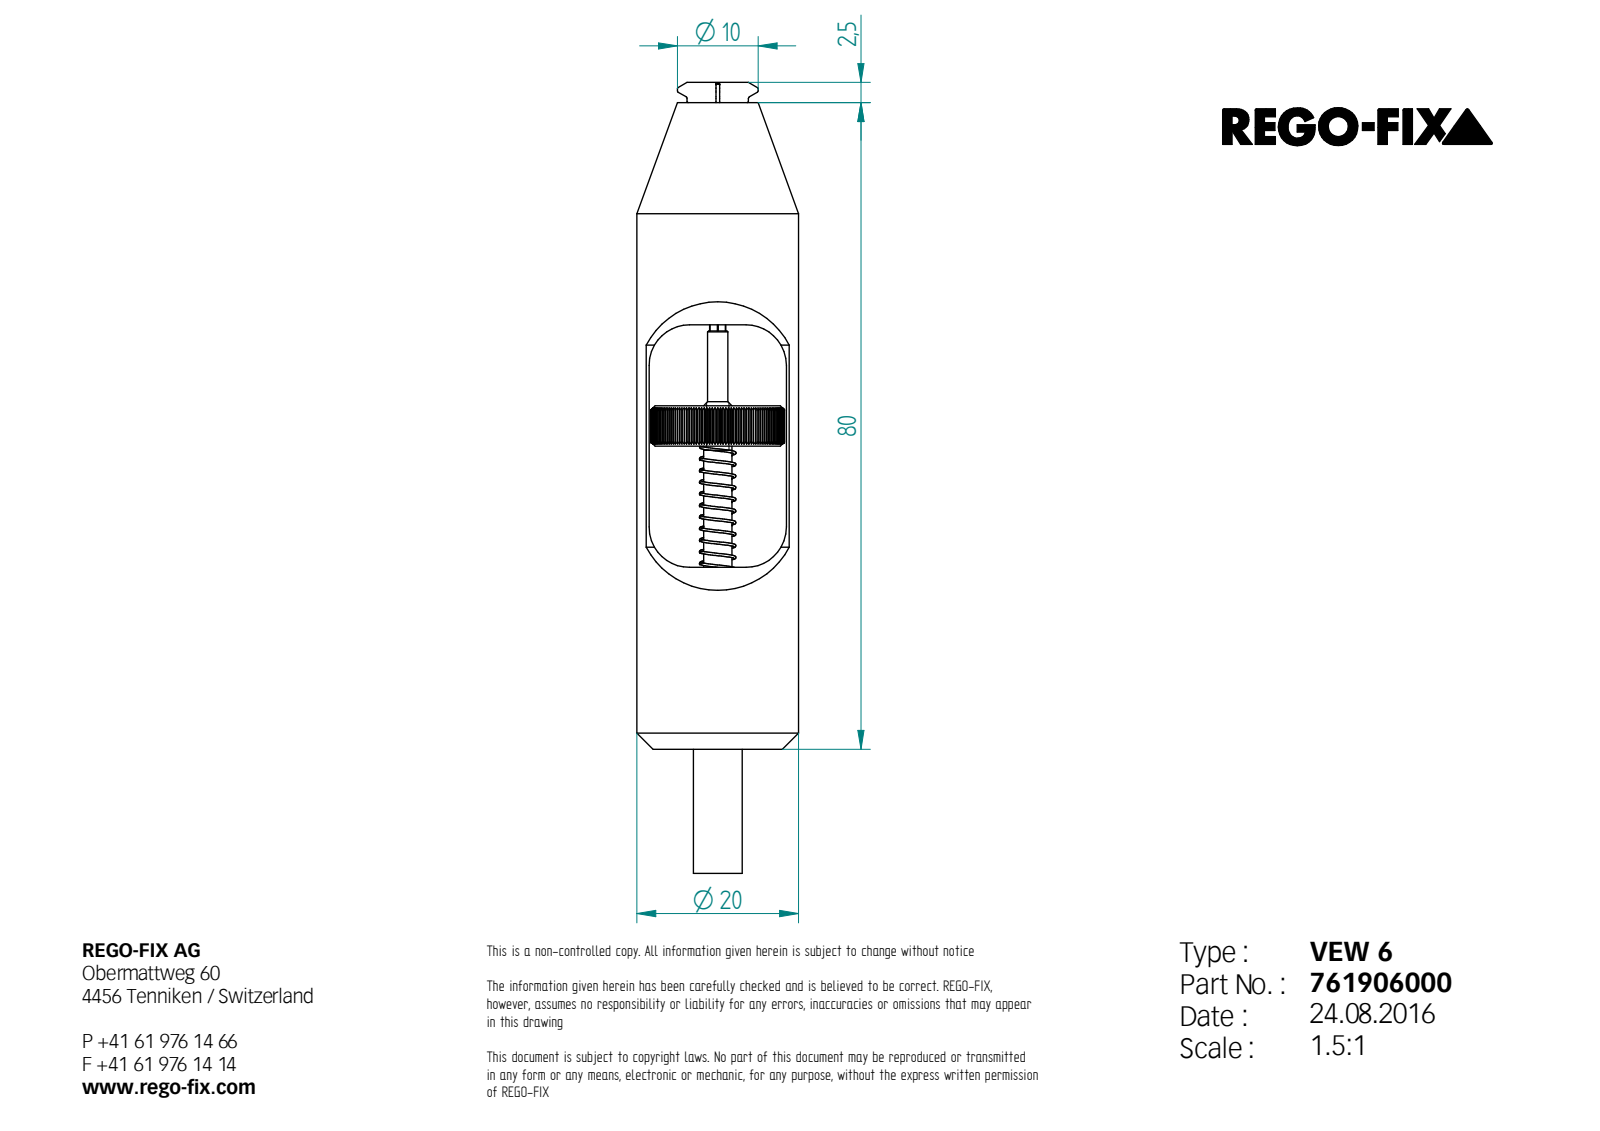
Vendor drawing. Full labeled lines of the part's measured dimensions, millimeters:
Part name (STEP PRODUCT): 0003544; 0002662; 0003533; 0003546 (+5 more)
STEP written by: Unknown (AUTOMOTIVE_DESIGN)
Units: millimetres
Bodies: 8 solids, 642 faces (380 planar, 202 cylindrical, 60 other)
Overall size (bounding box): 102.5 × 20 × 20
Volume: 15 914 mm³ · Surface area: 9 192 mm²
Round holes (diameter × count): ⌀1.5 ×1, ⌀2.05 ×1, ⌀2.85 ×1, ⌀3.17 ×1, ⌀3.46 ×1, ⌀4.4 ×1, ⌀6.35 ×1
Round bosses / shafts (diameter × count): ⌀20 ×1, ⌀10 ×1, ⌀7.6 ×1, ⌀6.2 ×1, ⌀6.1 ×1, ⌀5.8 ×1, ⌀4 ×1, ⌀3.5 ×1
Partial cylindrical surfaces — rounded edges, fillets, slot ends (radius × count): R0.52 ×4, R5 ×4, R0.15 ×2, R1.12 ×1, R1.44 ×1, R2.12 ×1, R8.25 ×1
Main face-to-face distances: 42.5, 37.5, 5, 17, 8, 15, 30, 11.1, 20, 22.5
